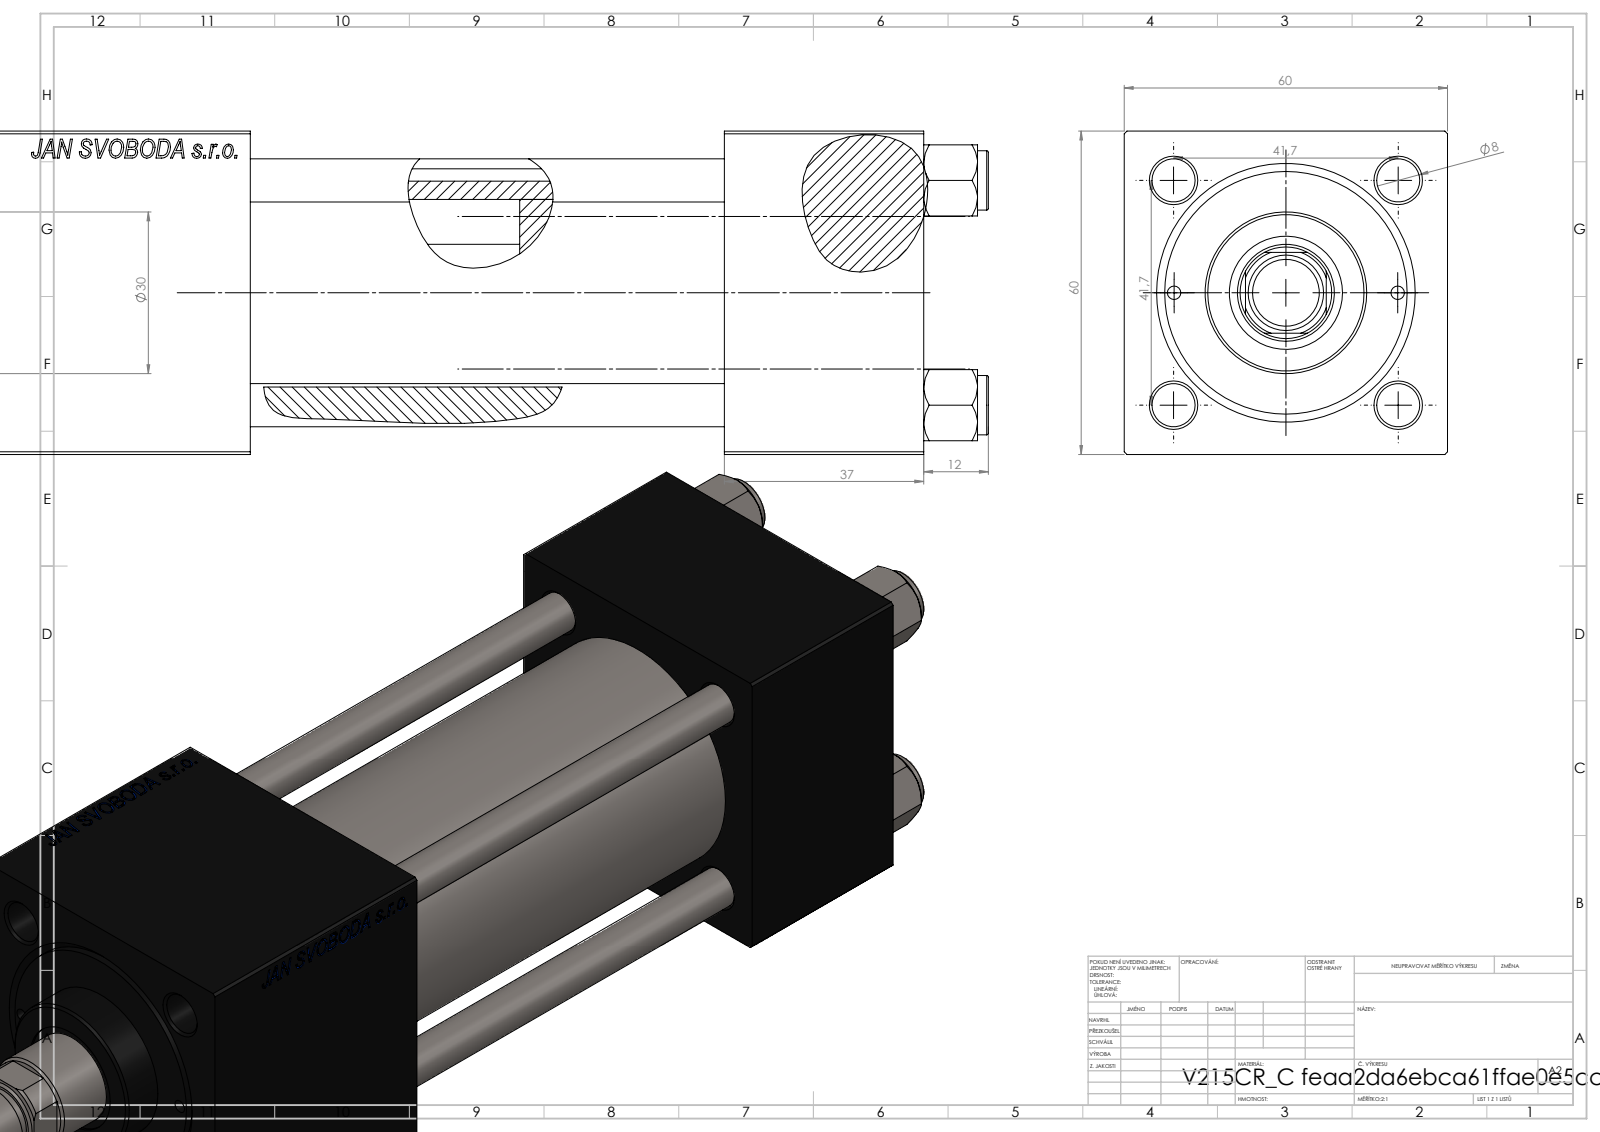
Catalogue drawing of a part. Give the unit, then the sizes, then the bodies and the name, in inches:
Units: inches
Overall size (bounding box): 9.173 × 2.362 × 2.362
Round holes (diameter × count): ⌀0.315 ×4, ⌀0.098 ×2, ⌀0.276 ×2, ⌀0.656 ×2, ⌀0.945 ×2, ⌀0.335 ×1, ⌀0.709 ×1, ⌀0.827 ×1, ⌀1.22 ×1, ⌀1.575 ×1, ⌀1.772 ×1
Round bosses / shafts (diameter × count): ⌀0.433 ×4, ⌀1.811 ×1, ⌀1.181 ×1, ⌀0.551 ×1, ⌀0.472 ×1
Partial cylindrical surfaces — rounded edges, fillets, slot ends (radius × count): R0.335 ×1
Main face-to-face distances: 2.362, 1.457, 7.008, 5.551, 2.087, 4.921, 3.465, 5.878, 4.421, 0.957
Hole centre spacings: 0.821, 1.161, 1.642, 1.832, 0.817, 2.322, 1.634, 4.823
Volume: 26.3 in³ · Surface area: 185 in²
Bodies: 12 solids, 1168 faces (532 planar, 94 cylindrical, 542 other)
Part name (STEP PRODUCT): V215CR_C_TYCINKA; V215CR_C_Body; NUT_M5_C; V215_VC_A (+2 more)
STEP written by: SolidWorks 2019 (CONFIG_CONTROL_DESIGN)
